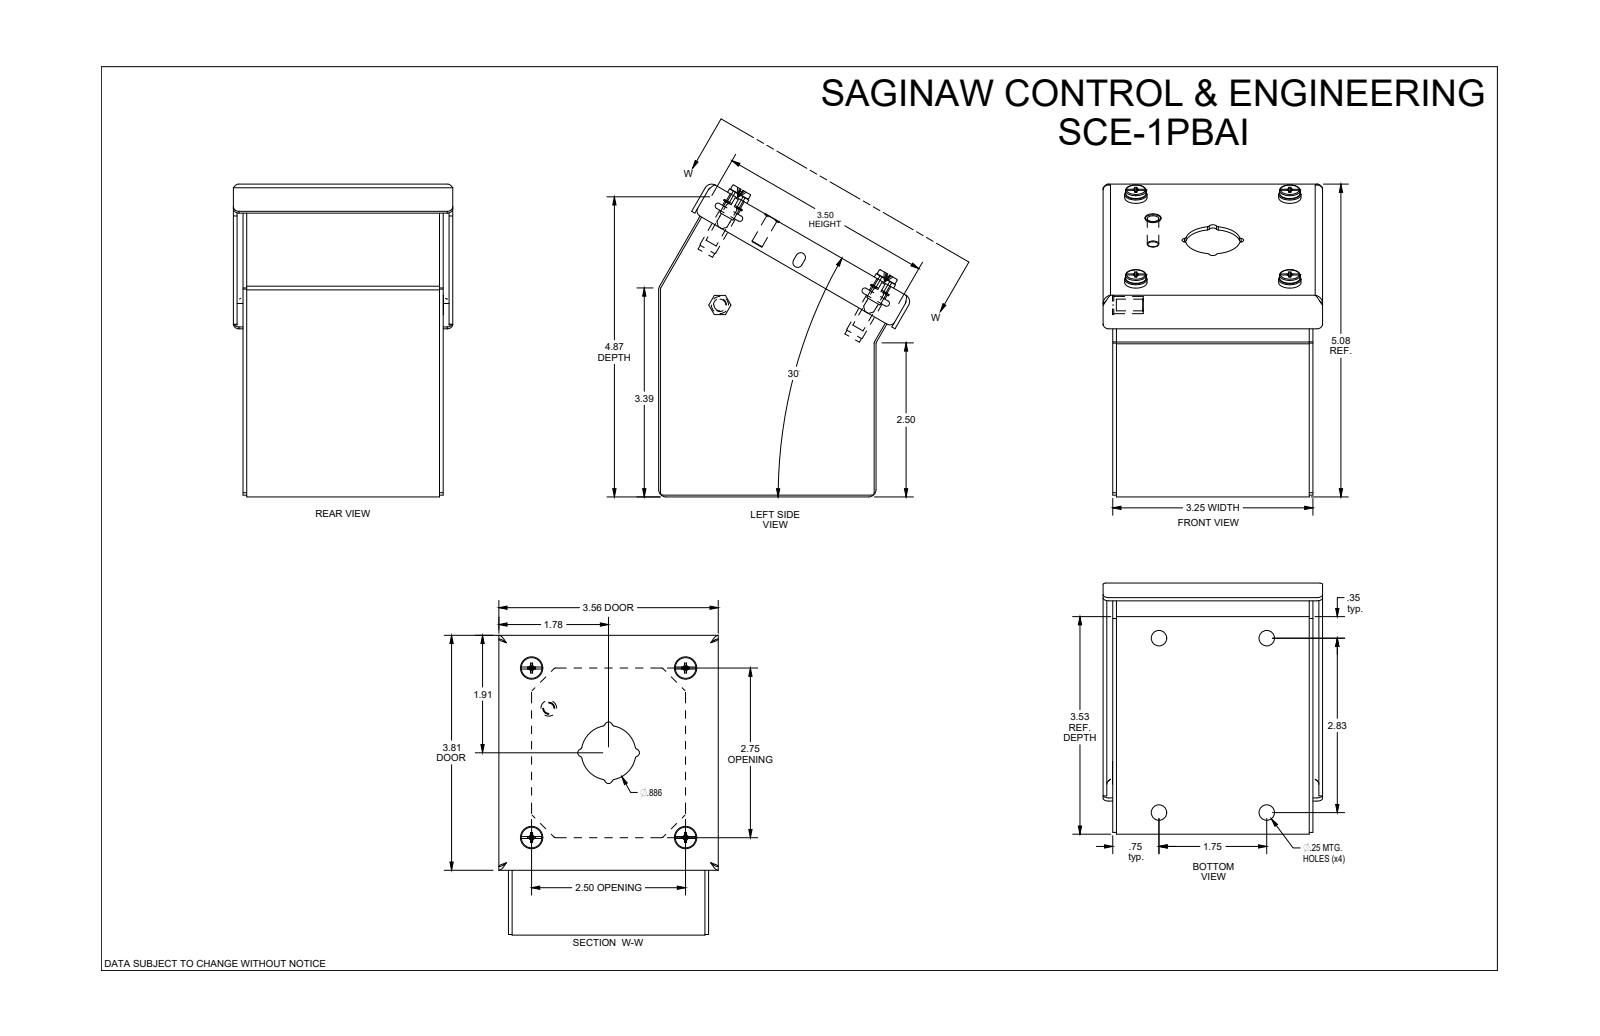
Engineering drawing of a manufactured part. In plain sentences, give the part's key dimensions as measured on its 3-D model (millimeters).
The part is named "SCE-1PBAI". Its 3-D file was written by "SolidWorks 2021 (AUTOMOTIVE_DESIGN)". It is 19 solids with 612 faces: 240 planar, 200 cylindrical and 172 other. Overall it measures 129.5 by 104.1 by 90.5 millimeters. Its volume is 96 140 cubic millimeters and its surface area 129 800 square millimeters. Round holes: 8 of diameter 6.4, 5 of diameter 4.8, 4 of diameter 5.6, 4 of diameter 6.8, 4 of diameter 8.1. Round bosses or shafts: 6 of diameter 7.4, 5 of diameter 4.8, 4 of diameter 9.2, 4 of diameter 8.6, 4 of diameter 8.5, 4 of diameter 6.9, 4 of diameter 6.6, 4 of diameter 3.7. Partial cylindrical surfaces (rounded edges, fillets, slot ends): 20 of radius 1.5, 12 of radius 0.8, 12 of radius 1, 10 of radius 0.3, 8 of radius 2.9, 8 of radius 6.1, 6 of radius 3, 4 of radius 1.6. The main face-to-face distances are 1.5, 81, 88.1, 79.5, 82.6, 4, 86.6, 89.7, 85, 1.5. The hole center spacings are 63.5, 69.9, 69.9, 94.4, 94.5, 44.5, 71.9, 84.5.
